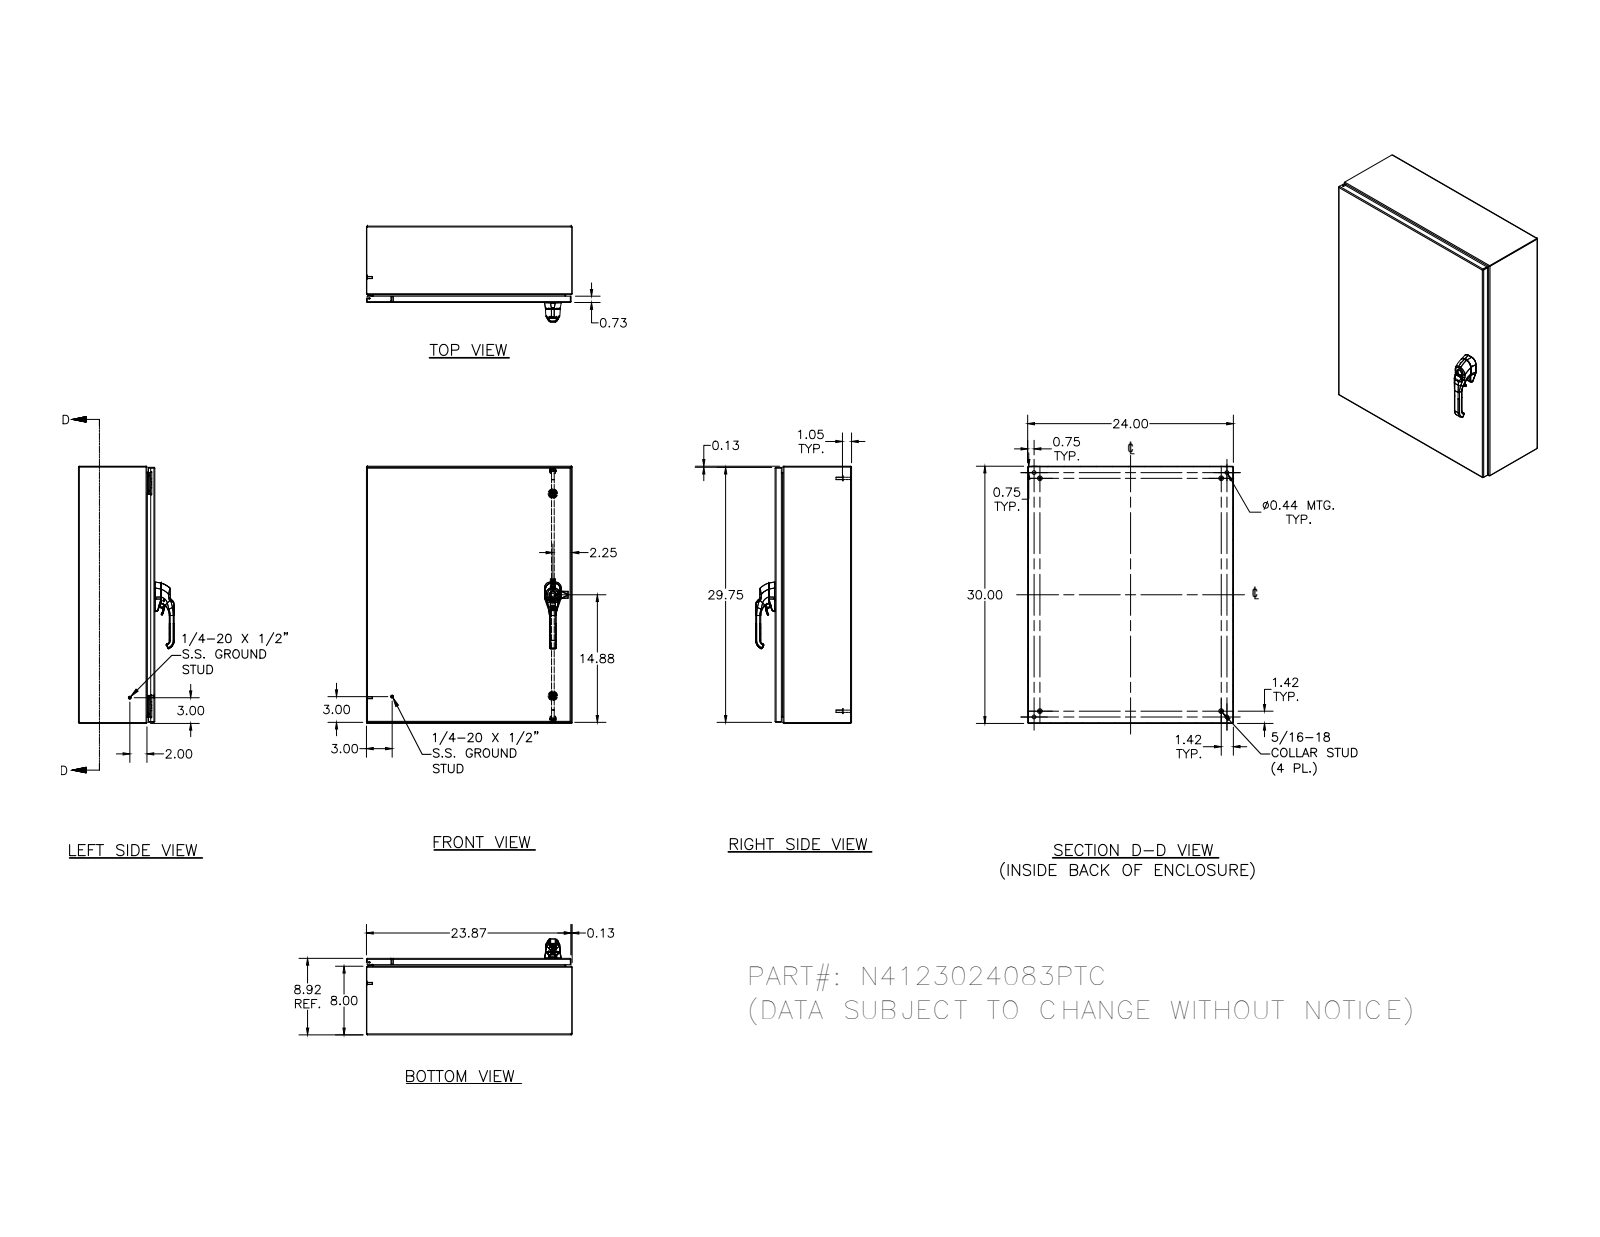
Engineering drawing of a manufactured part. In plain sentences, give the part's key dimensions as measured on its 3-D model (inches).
The part is named "N4123024083PTC; N4123024083PTCBKP; N41230243PTCLID; HFW328176 (+8 more)". Its 3-D file was written by "Autodesk Inventor 2011 (AUTOMOTIVE_DESIGN)". It is 49 solids with 2962 faces: 941 planar, 1101 cylindrical and 920 other. Overall it measures 30 by 24 by 11.186 inches. Its volume is 189.7 cubic inches and its surface area 5 204 square inches. Round holes: 5 of diameter 0.188, 4 of diameter 0.093, 4 of diameter 0.152, 4 of diameter 0.165, 4 of diameter 0.167, 4 of diameter 0.172, 4 of diameter 0.197, 4 of diameter 0.437, 3 of diameter 0.213, 3 of diameter 0.236, 3 of diameter 0.354, 2 of diameter 0.106. Round bosses or shafts: 10 of diameter 0.25, 4 of diameter 0.563, 4 of diameter 0.36, 4 of diameter 0.32, 4 of diameter 0.3, 4 of diameter 0.275, 4 of diameter 0.256, 4 of diameter 0.236. Partial cylindrical surfaces (rounded edges, fillets, slot ends): 180 of radius 0.02, 80 of radius 0.012, 33 of radius 0.118, 30 of radius 0.031, 26 of radius 0.05, 20 of radius 0.105, 19 of radius 0.019, 18 of radius 0.016. The main face-to-face distances are 0.074, 8.843, 8.917, 8.769, 23.926, 29.926, 23.852, 24, 30, 29.852. The hole center spacings are 25.996, 22.869, 0.017, 0.66, 26.656, 0.019, 0.177, 0.5.
